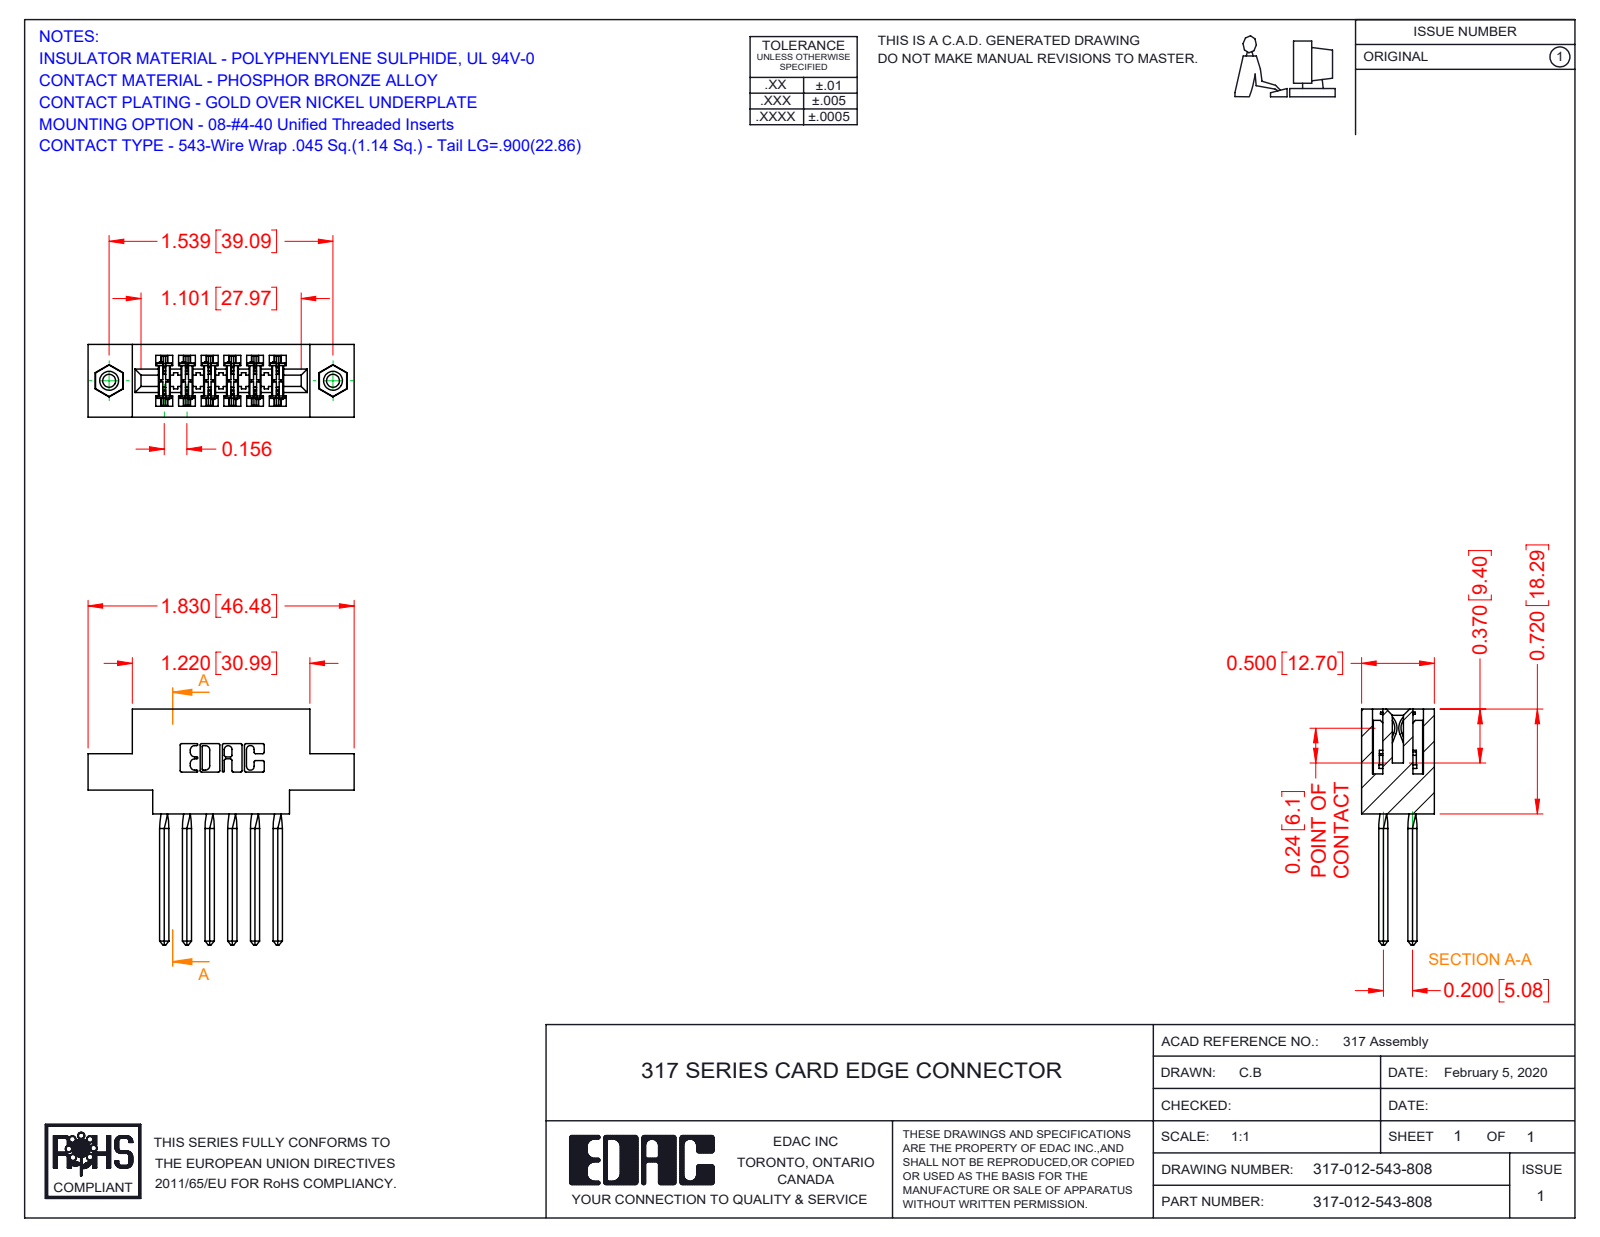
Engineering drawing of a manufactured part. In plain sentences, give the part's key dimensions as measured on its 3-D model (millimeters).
The part is named "345-250-001_345-250-003-102; 317-012-543-808; 317 Part_.156 Dia - TI; 317-290-001_543". Its 3-D file was written by "SolidWorks 2016 (CONFIG_CONTROL_DESIGN)". It is 15 solids with 1230 faces: 966 planar, 200 cylindrical and 64 other. Overall it measures 46.5 by 41.1 by 12.7 millimeters. Its volume is 6 640 cubic millimeters and its surface area 8 677 square millimeters. Round holes: 2 of diameter 2.3, 2 of diameter 3.2, 2 of diameter 4. Round bosses or shafts: 2 of diameter 3.9. Partial cylindrical surfaces (rounded edges, fillets, slot ends): 24 of radius 0.4, 22 of radius 0.3, 6 of radius 0.2, 6 of radius 0.8, 3 of radius 0.7, 2 of radius 2.4, 2 of radius 2.5, 2 of radius 2.8. The main face-to-face distances are 2.8, 12.7, 1.9, 5.6, 10.8, 1.7, 4, 3.6, 8.4, 2.9. The hole center spacings are 39.1.
